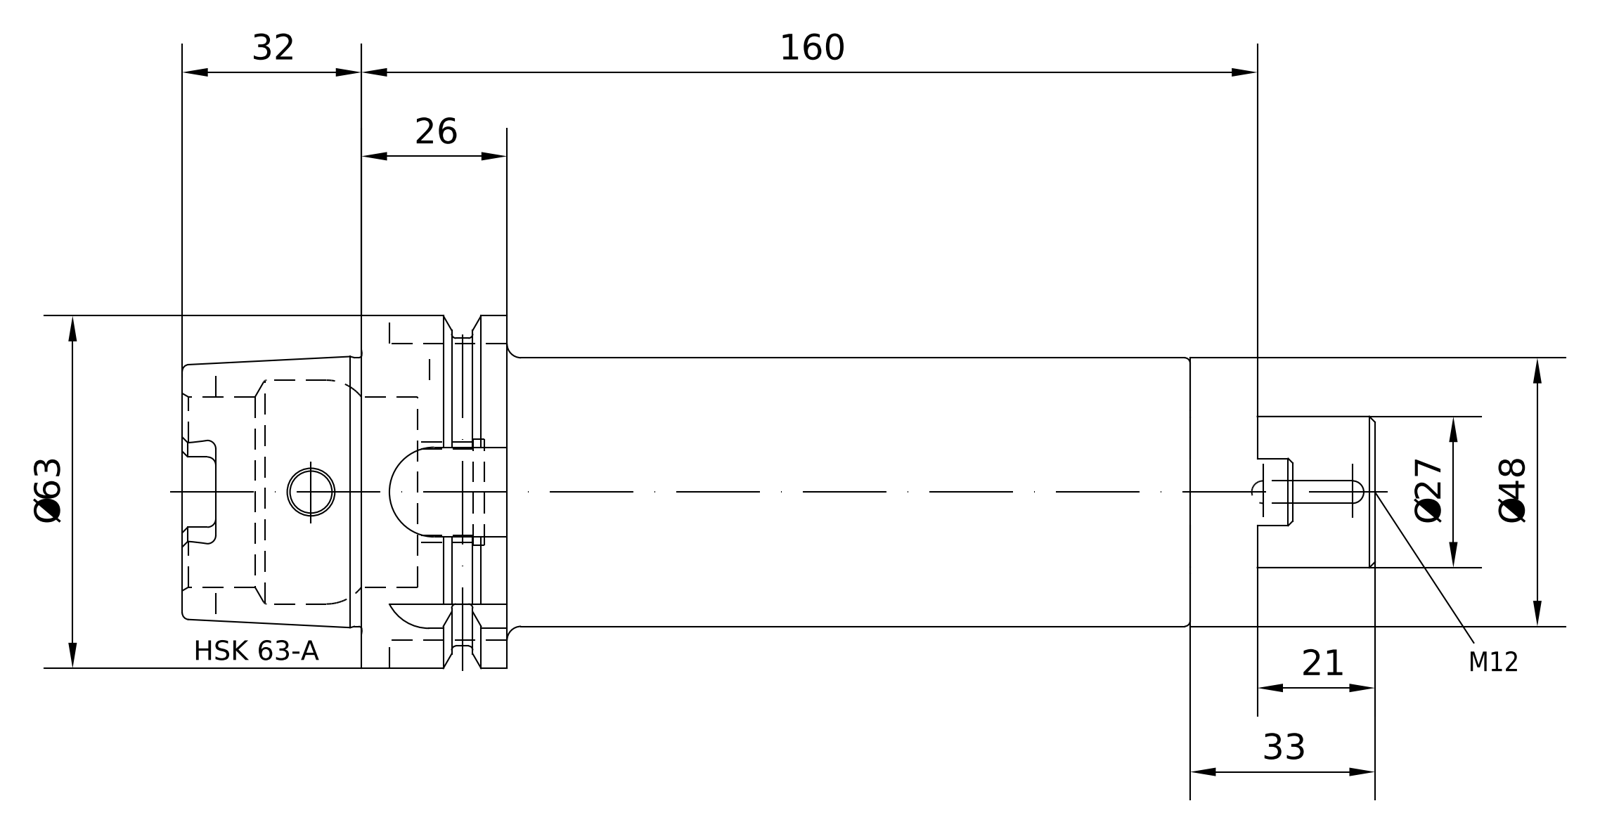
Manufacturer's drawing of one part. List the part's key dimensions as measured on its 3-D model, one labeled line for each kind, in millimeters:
Part name (STEP PRODUCT): A63-042-27; 85-200-27; A63-042-27_ASM
STEP written by: PRO/ENGINEER BY PARAMETRIC TECHNOLOGY CORPORATION, 2010430 (CONFIG_CONTROL_DESIGN)
Units: millimetres
Bodies: 2 solids, 266 faces (124 planar, 64 cylindrical, 78 other)
Overall size (bounding box): 213 × 63 × 63
Volume: 330 151 mm³ · Surface area: 53 051 mm²
Round holes (diameter × count): ⌀7.5 ×1, ⌀10 ×1, ⌀10.2 ×1, ⌀12 ×1, ⌀16.92 ×1, ⌀18.32 ×1, ⌀18.66 ×1, ⌀27.36 ×1, ⌀31.5 ×1, ⌀34 ×1, ⌀40 ×1
Round bosses / shafts (diameter × count): ⌀63 ×1, ⌀55 ×1, ⌀48.04 ×1, ⌀48 ×1, ⌀27 ×1, ⌀18 ×1
Partial cylindrical surfaces — rounded edges, fillets, slot ends (radius × count): R1.5 ×6, R3 ×4, R3.5 ×2, R6.05 ×1, R8 ×1, R8.02 ×1, R9.02 ×1
Main face-to-face distances: 148, 26, 10, 122, 160, 134, 12, 181, 32, 16
